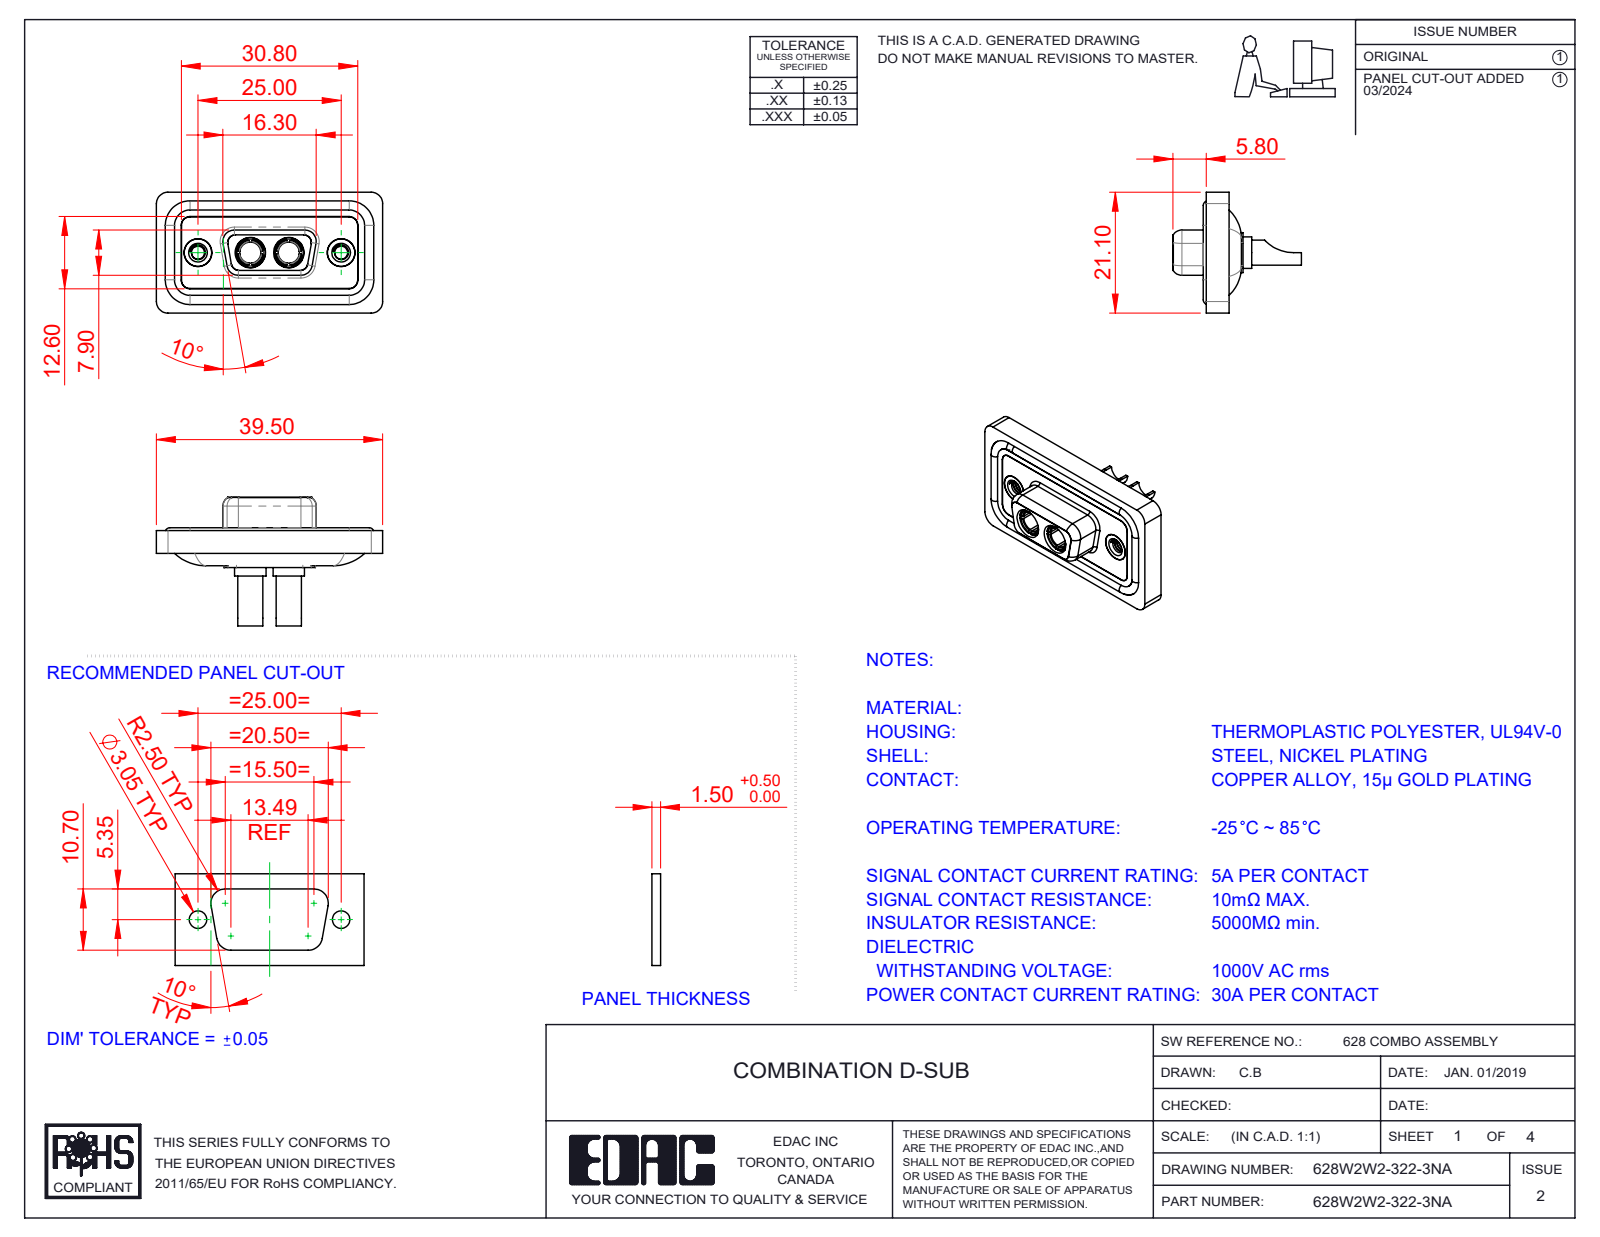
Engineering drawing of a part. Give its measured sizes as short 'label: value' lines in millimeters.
name: 628Combo Shell Rear_09 Contacts; 628W2W2-322-3NA; 628Combo Housing_2W2; 628Combo Waterproof Housing_09 Contacts (+3 more)
written by: SolidWorks 2023 (CONFIG_CONTROL_DESIGN)
unit: mm
bodies: 11 solids, 544 faces (169 planar, 242 cylindrical, 133 other)
size: 39.5 × 22.45 × 21.1
volume: 4 762 mm³; area: 7 848 mm²
holes: 4× ⌀4.85, 2× ⌀2.26, 2× ⌀3.5, 2× ⌀3.7, 2× ⌀4, 2× ⌀4.05, 2× ⌀5, 2× ⌀5.3
bosses: 4× ⌀1.6, 2× ⌀5.5, 2× ⌀5.2, 2× ⌀4.96, 2× ⌀4.95, 2× ⌀4.8, 2× ⌀4.75, 2× ⌀4.4
rounds: 22× R1.5, 18× R2, 8× R1.35, 8× R1.6, 4× R0.25, 4× R0.5, 4× R0.6, 4× R0.65
face distances: 0.4, 1.1, 2.9, 1.8, 0.5, 1.6, 5.65, 7.45, 5.35, 3.1
hole spacings: 9.14, 15.86, 6.72, 25
